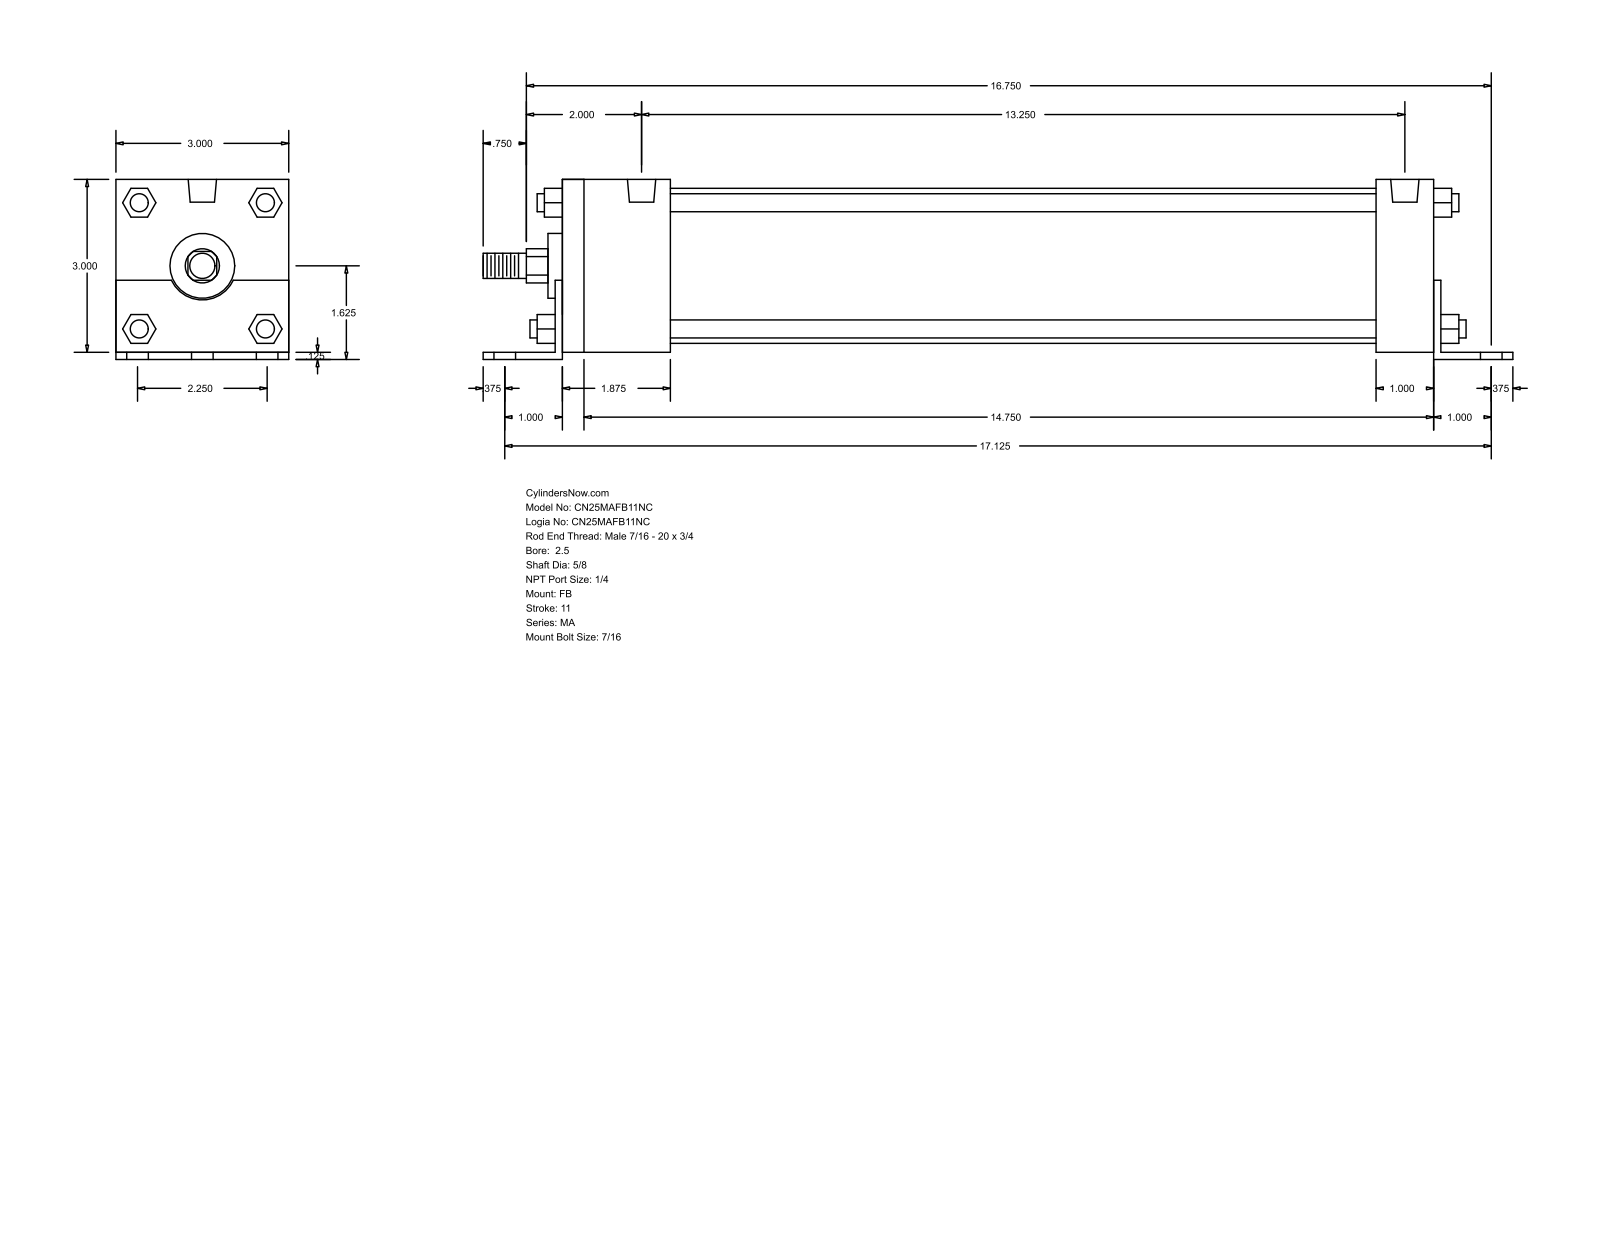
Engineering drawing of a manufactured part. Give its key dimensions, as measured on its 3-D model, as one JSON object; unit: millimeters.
{"part_name": "MA_FB__0250_0.625", "step_written_by": "GSSL Pune (CONFIG_CONTROL_DESIGN)", "units": "millimeters", "bodies": {"solids": 0, "faces": 140, "planar": 105, "cylindrical": 35, "other": 0}, "overall_size": [454.02, 79.38, 76.2], "round_holes": [[11.11, 6], [7.94, 4], [12.49, 2]], "round_bosses_or_shafts": [[7.94, 4], [68.33, 1], [28.57, 1], [15.88, 1], [11.11, 1]], "partial_cylinders_radius": [[7.54, 1], [15.05, 1]], "face_to_face_distances": [76.2, 3.17, 79.37, 3.18, 387.35, 384.17, 28.58, 47.62, 25.4, 390.53], "hole_center_spacings": [28.57, 435.92, 434.98, 47.62, 57.14, 66.75, 336.55, 375.74]}
